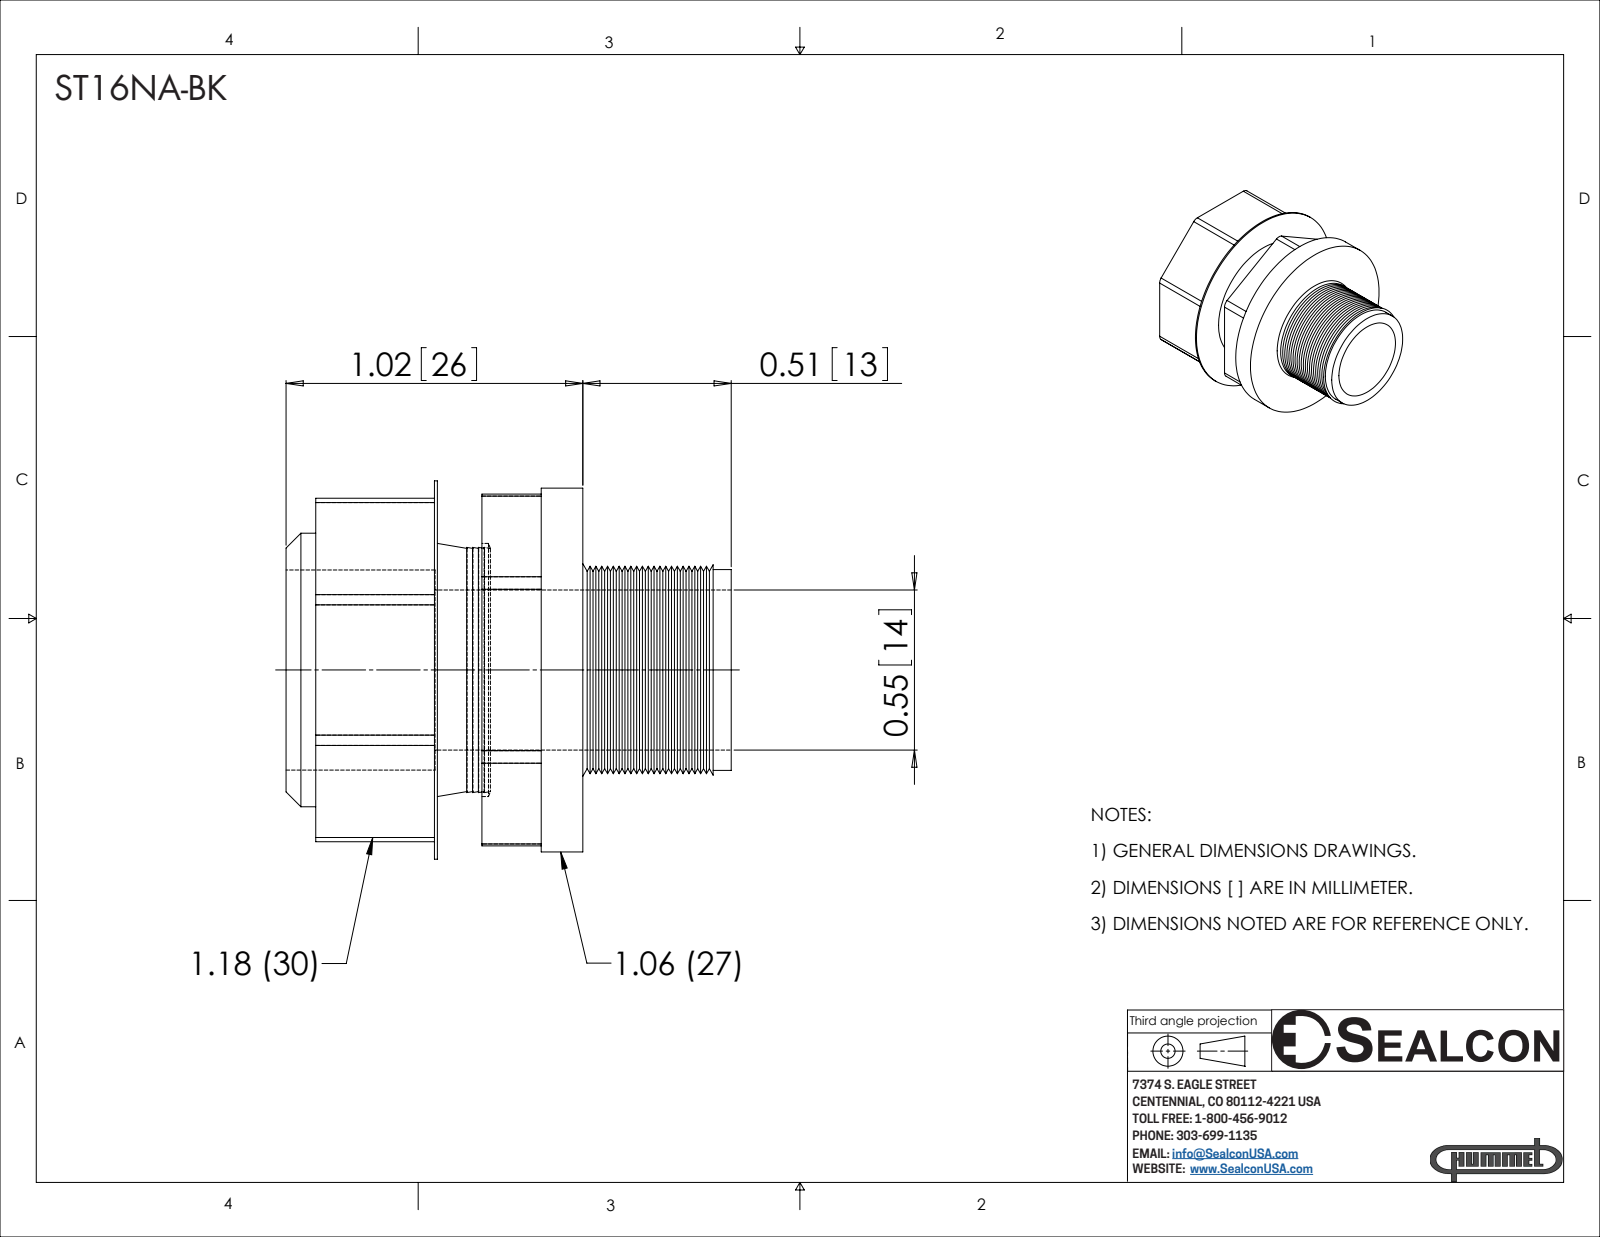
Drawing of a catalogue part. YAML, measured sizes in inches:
part_name: "ST16NA-BK"
step_written_by: "SolidWorks 2008 (CONFIG_CONTROL_DESIGN)"
units: inches
bodies: {solids: 2, faces: 165, planar: 25, cylindrical: 30, other: 110}
overall_size: [1.53, 1.3, 1.3]
volume: 0.772
surface_area: 12.91
round_holes:
  - {diameter: 0.55, count: 1}
  - {diameter: 0.687, count: 1}
  - {diameter: 0.87, count: 1}
round_bosses_or_shafts:
  - {diameter: 1.3, count: 1}
  - {diameter: 1.25, count: 1}
  - {diameter: 0.94, count: 1}
  - {diameter: 0.69, count: 1}
partial_cylinders:
  - {radius: 0.05, count: 14}
face_to_face_distances: [0.5, 0.418, 0.918, 0.571, 0.153, 0.347, 1.18, 1.18, 1.06, 1.02]
